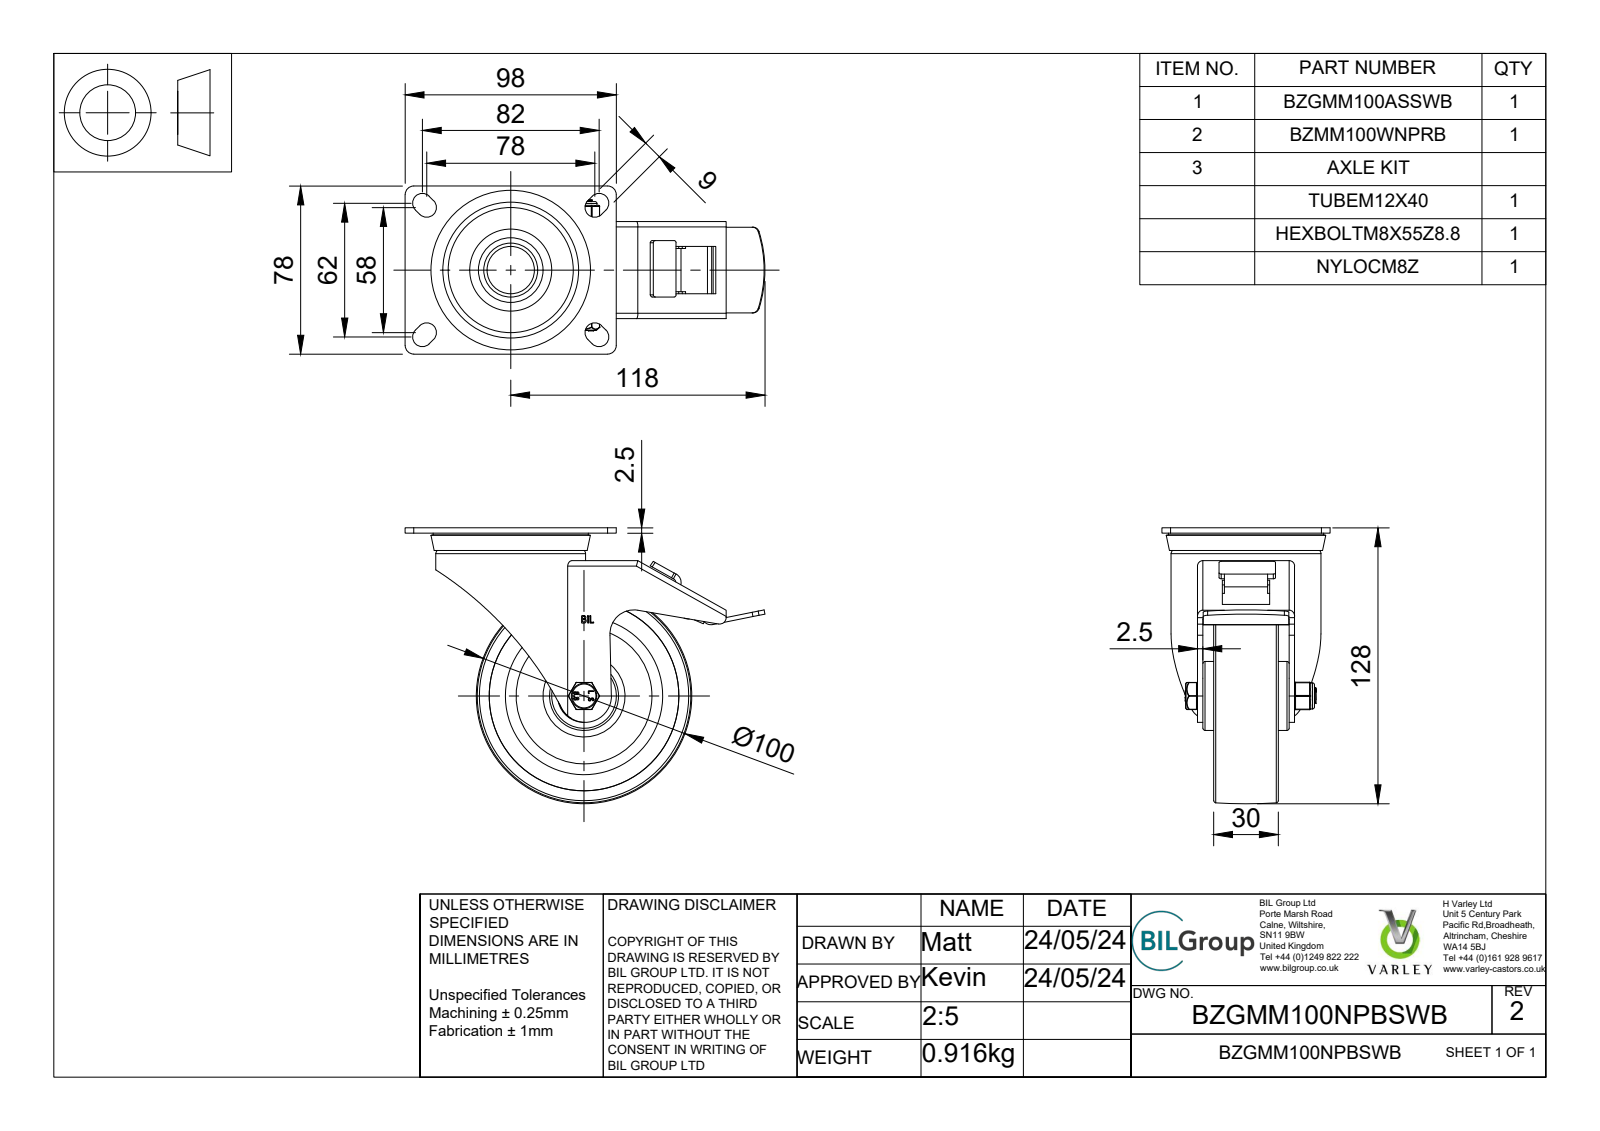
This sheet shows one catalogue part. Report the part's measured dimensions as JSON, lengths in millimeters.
{"part_name": "BZGMM100NPBSWB - 2 v3; BZGMM100ASSWB - 2 v1; ZINC PLATED, PRESSED STEEL FORKS; BRAKE PAD (+7 more)", "step_written_by": "Autodesk Translation Framework v13.14.0.145 (AUTOMOTIVE_DESIGN)", "units": "millimeters", "bodies": {"solids": 47, "faces": 549, "planar": 242, "cylindrical": 187, "other": 120}, "overall_size": [167, 128, 78], "volume_mm3": 247591, "surface_area_mm2": 138698, "round_holes": [[0.66, 2], [8, 1], [8.2, 1], [8.4, 1], [8.6, 1], [12.5, 1], [16, 1], [23.5, 1], [24.5, 1], [26, 1], [30, 1], [64.5, 1]], "round_bosses_or_shafts": [[5.5, 6], [69.5, 1], [47, 1], [32, 1], [25, 1], [24, 1], [22.5, 1], [12.1, 1]], "partial_cylinders_radius": [[0.5, 18], [0.25, 12], [1.25, 8], [4.5, 8], [4, 5], [0.33, 4], [0.64, 4], [1, 4]], "face_to_face_distances": [2.5, 7.5, 35, 5, 37.5, 42.5, 22, 13, 17, 20.5], "hole_center_spacings": [3.22, 2.49]}
